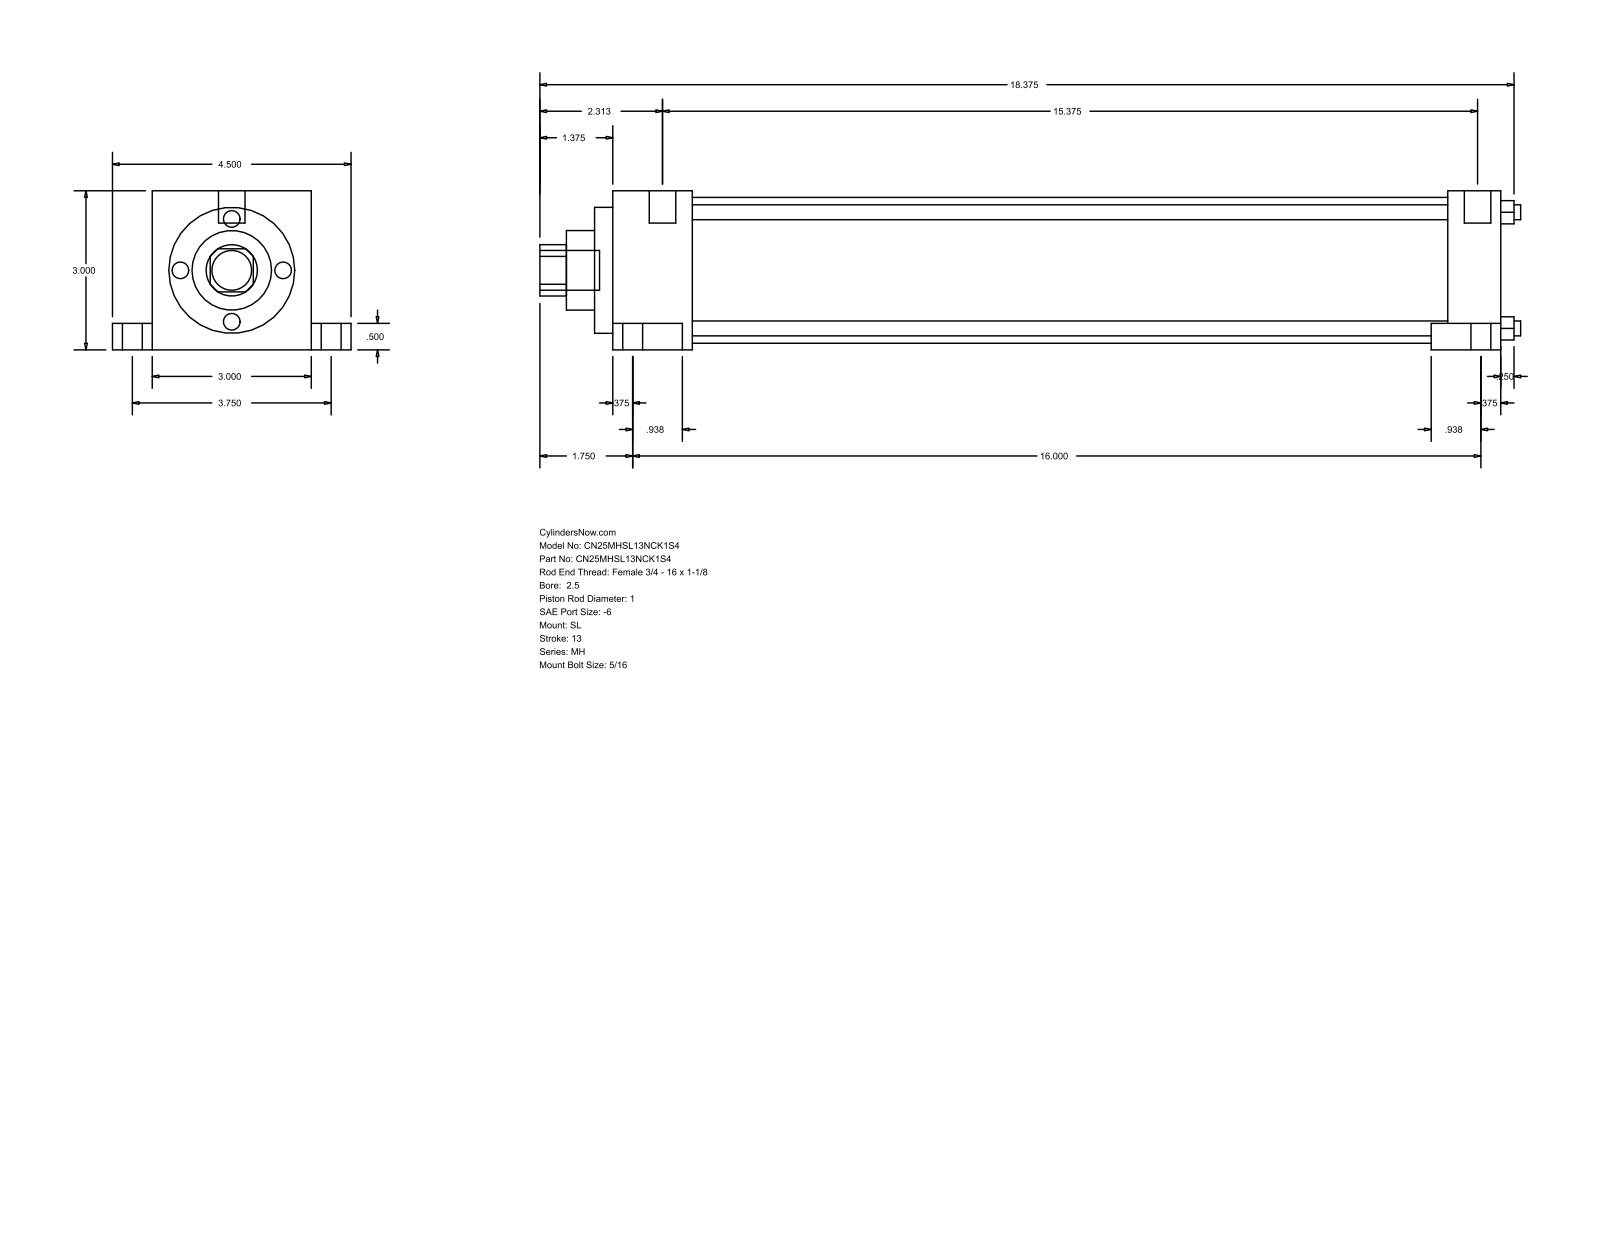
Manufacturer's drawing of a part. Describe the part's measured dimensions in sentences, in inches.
The part is named "MH_SL__0250_1". Its 3-D file was written by "GSSL Pune (CONFIG_CONTROL_DESIGN)". It is 0 solids with 86 faces: 61 planar, 25 cylindrical and 0 other. Overall it measures 18.5 by 4.5 by 3 inches. Round holes: 4 of diameter 0.281, 1 of diameter 1, 1 of diameter 1.5, 1 of diameter 2.375, 1 of diameter 2.75. Round bosses or shafts: 2 of diameter 0.625, 2 of diameter 0.375, 2 of diameter 0.219, 1 of diameter 0.75, 1 of diameter 0.5. Partial cylindrical surfaces (rounded edges, fillets, slot ends): 1 of radius 0.484. The main face-to-face distances are 3, 1, 16.094, 17.094, 0.5, 2.5, 0.75, 3.75, 0.531, 16.625. The hole center spacings are 1.548, 2.19, 3.097.
